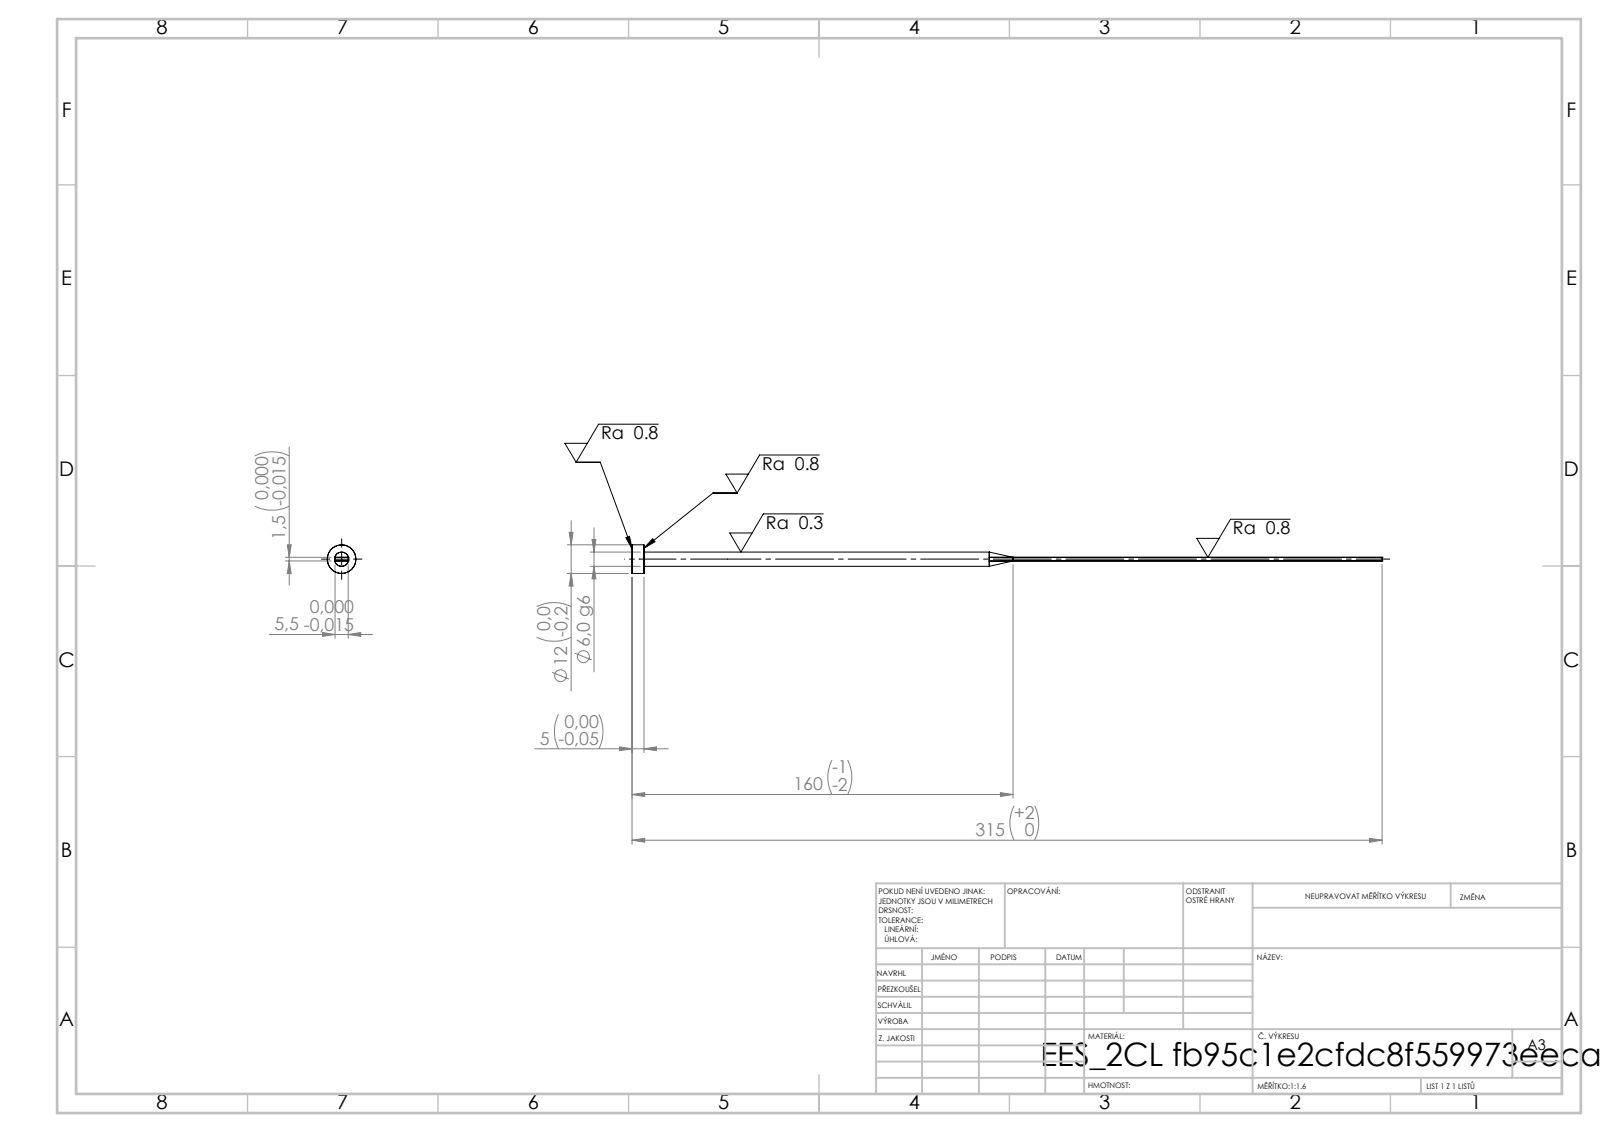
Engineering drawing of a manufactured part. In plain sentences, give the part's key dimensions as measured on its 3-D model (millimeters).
Its 3-D file was written by "SolidWorks 2019 (CONFIG_CONTROL_DESIGN)". It is 1 solid with 15 faces: 7 planar, 4 cylindrical and 4 other. Overall it measures 315 by 12 by 12 millimeters. Its volume is 6 119 cubic millimeters and its surface area 5 457 square millimeters. Round bosses or shafts: 1 of diameter 12, 1 of diameter 6. The main face-to-face distances are 1.5, 5.5, 5, 315, 310.
